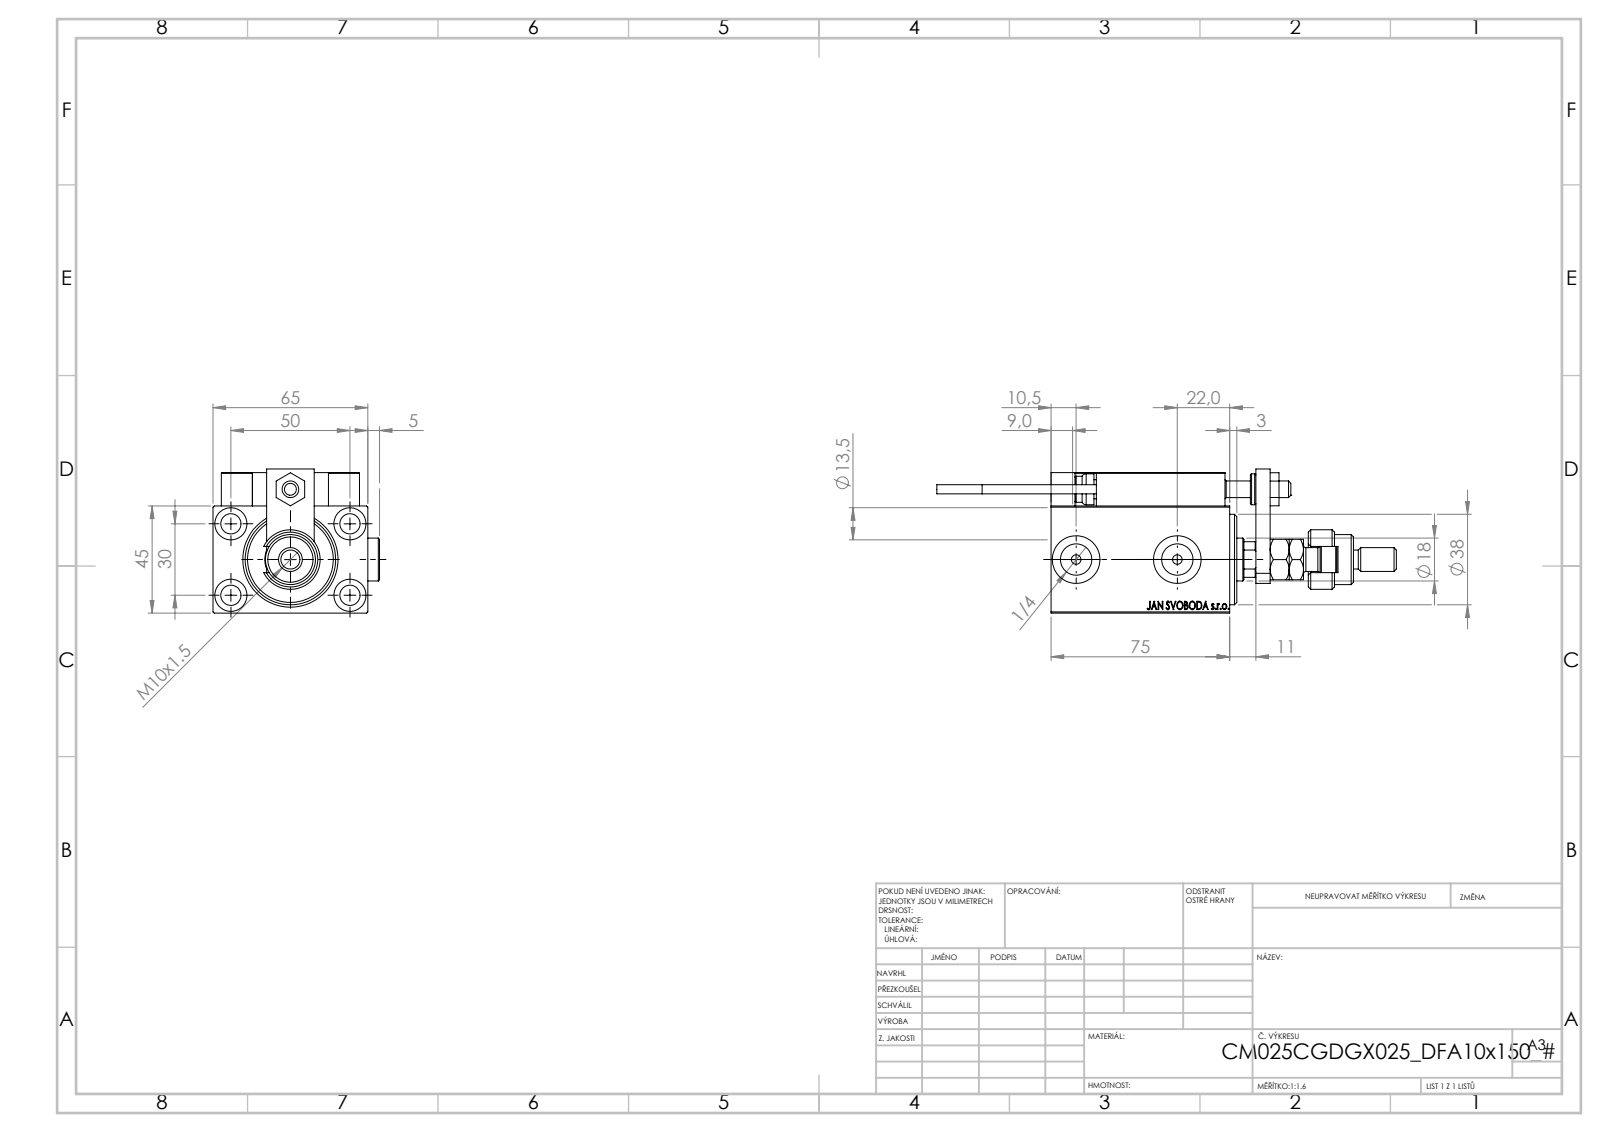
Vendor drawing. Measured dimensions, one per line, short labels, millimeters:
name: SWITCH DIM B,W; ALLEN BOLT D8; X_Y_DFA; NUT_D12 (+7 more)
written by: SolidWorks 2019 (CONFIG_CONTROL_DESIGN)
unit: mm
bodies: 27 solids, 1421 faces (622 planar, 217 cylindrical, 582 other)
size: 193 × 69.9 × 60.5
volume: 245 987 mm³; area: 79 949 mm²
holes: 6× ⌀4, 5× ⌀8, 5× ⌀8.5, 4× ⌀3.2, 4× ⌀13.5, 2× ⌀5, 2× ⌀13.16, 2× ⌀20, 1× ⌀7, 1× ⌀14.5, 1× ⌀18, 1× ⌀21.5
bosses: 2× ⌀18, 2× ⌀5, 2× ⌀3.8, 1× ⌀25, 1× ⌀21, 1× ⌀16, 1× ⌀13, 1× ⌀11
rounds: 30× R0.3, 2× R3, 1× R5.5, 1× R8.5, 1× R8.75
face distances: 45, 14, 65, 6, 59, 3, 19, 13, 5, 64
hole spacings: 29.15, 11.37, 20, 27.07, 28.9, 29.59, 29.69, 30
